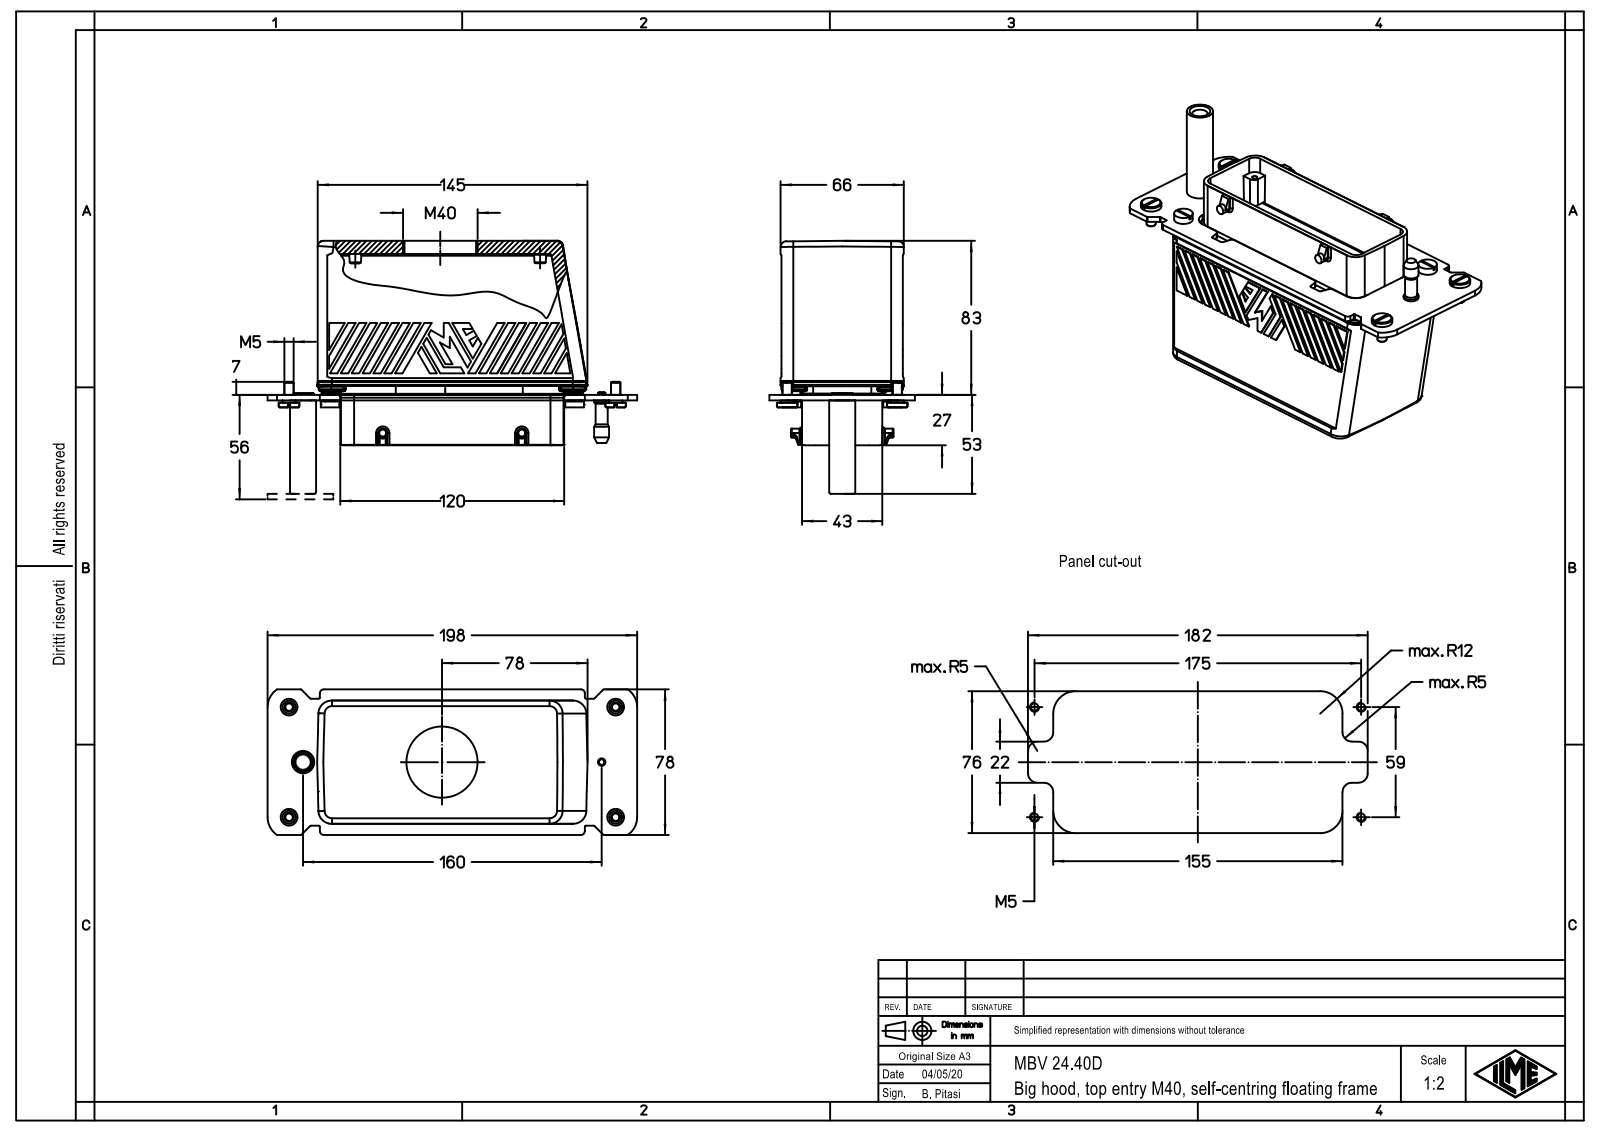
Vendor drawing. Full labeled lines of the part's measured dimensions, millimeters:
Part name (STEP PRODUCT): MBV 24.40D
STEP written by: Creo Elements/Direct Modeling 20.1B 02-Apr-2019 (C) Parametric Technology GmbH (AUTOMOTIVE_DESIGN)
Units: millimetres
Bodies: 1 solid, 924 faces (474 planar, 230 cylindrical, 220 other)
Overall size (bounding box): 198 × 135.21 × 78
Volume: 754 258 mm³ · Surface area: 96 724 mm²
Round holes (diameter × count): ⌀9 ×4, ⌀5.1 ×2, ⌀7.2 ×2, ⌀4.05 ×1, ⌀8.2 ×1, ⌀9.6 ×1, ⌀12.05 ×1, ⌀40 ×1
Round bosses / shafts (diameter × count): ⌀5 ×6, ⌀11 ×4, ⌀7 ×4, ⌀10 ×2, ⌀9.3 ×2, ⌀4.8 ×2, ⌀14 ×1, ⌀12 ×1
Partial cylindrical surfaces — rounded edges, fillets, slot ends (radius × count): R1 ×52, R0.5 ×20, R7 ×16, R2 ×14, R0.3 ×6, R1.5 ×6, R3 ×6, R4.2 ×4
Main face-to-face distances: 3, 85.21, 82.21, 65.01, 54, 11.01, 0.4, 11.41, 54.4, 65.41
Hole centre spacings: 30.44, 170.08, 22.14, 30.65, 59, 60.63, 147.98, 153.02
